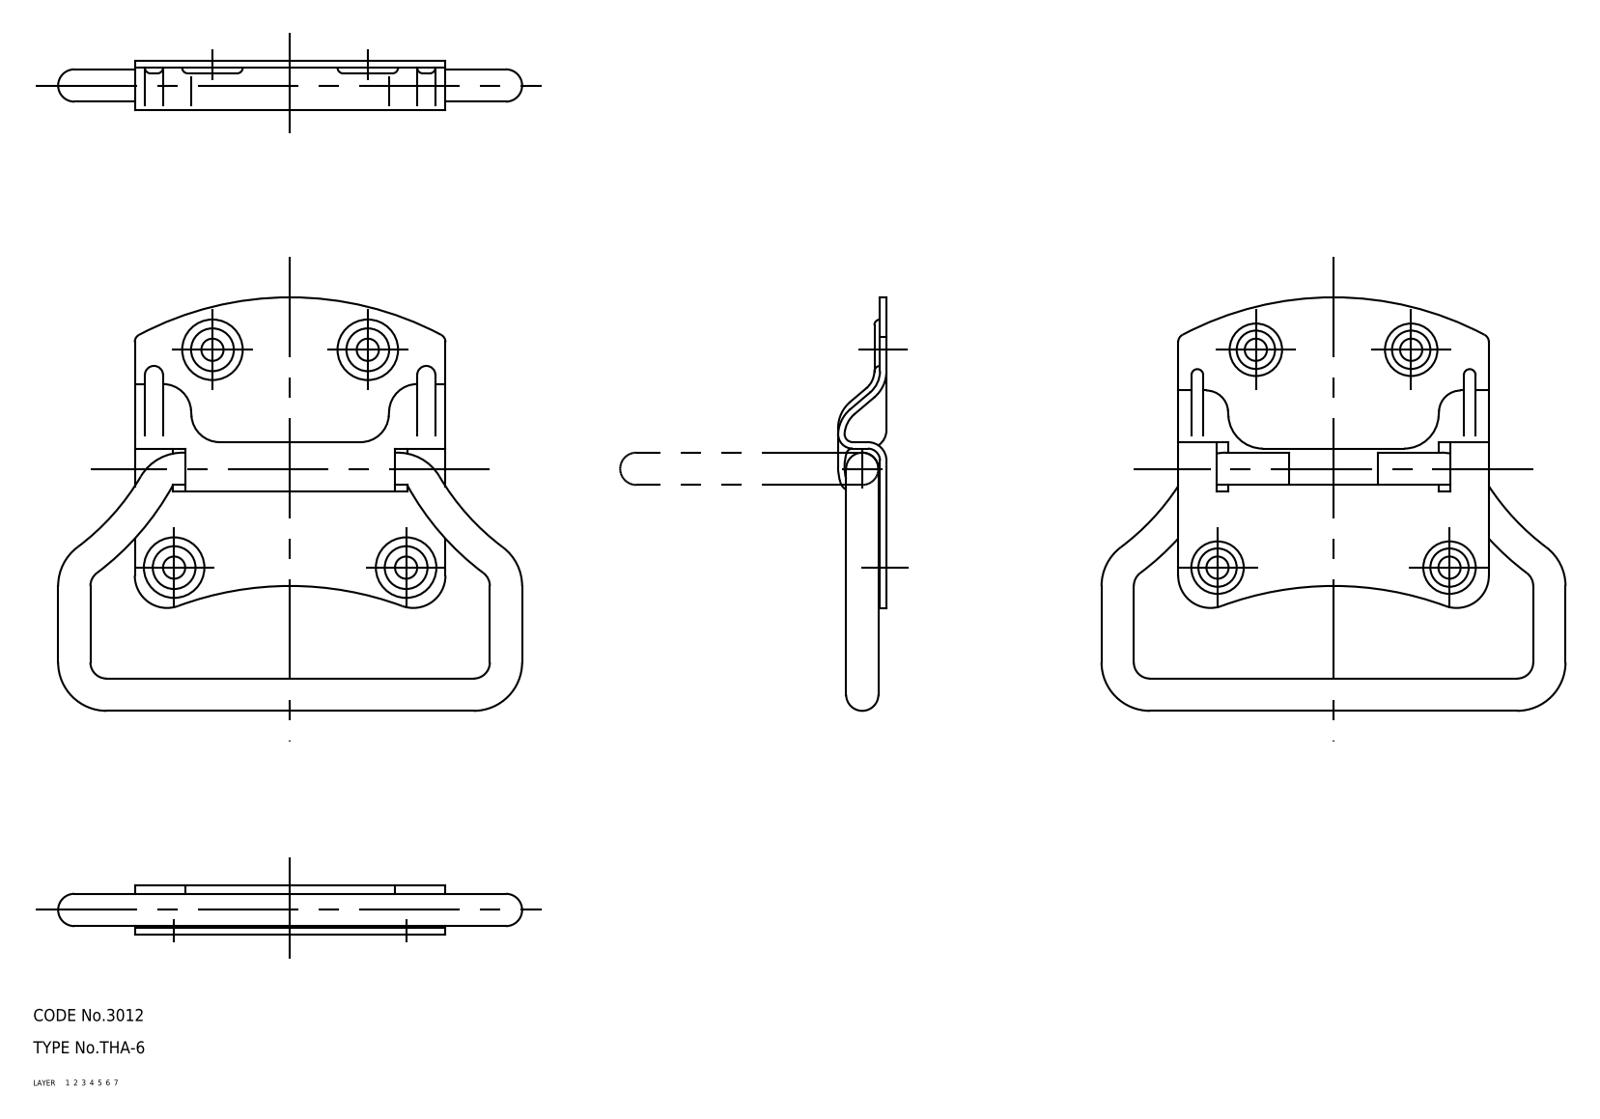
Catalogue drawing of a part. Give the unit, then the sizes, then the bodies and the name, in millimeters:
Units: millimetres
Overall size (bounding box): 115 × 102.5 × 12
Volume: 23 853 mm³ · Surface area: 20 957 mm²
Bodies: 2 solids, 266 faces (0 planar, 0 cylindrical, 266 other)
Part name (STEP PRODUCT): grip; base; THA_6_3193_36
STEP written by: CADfix (AUTOMOTIVE_DESIGN)
